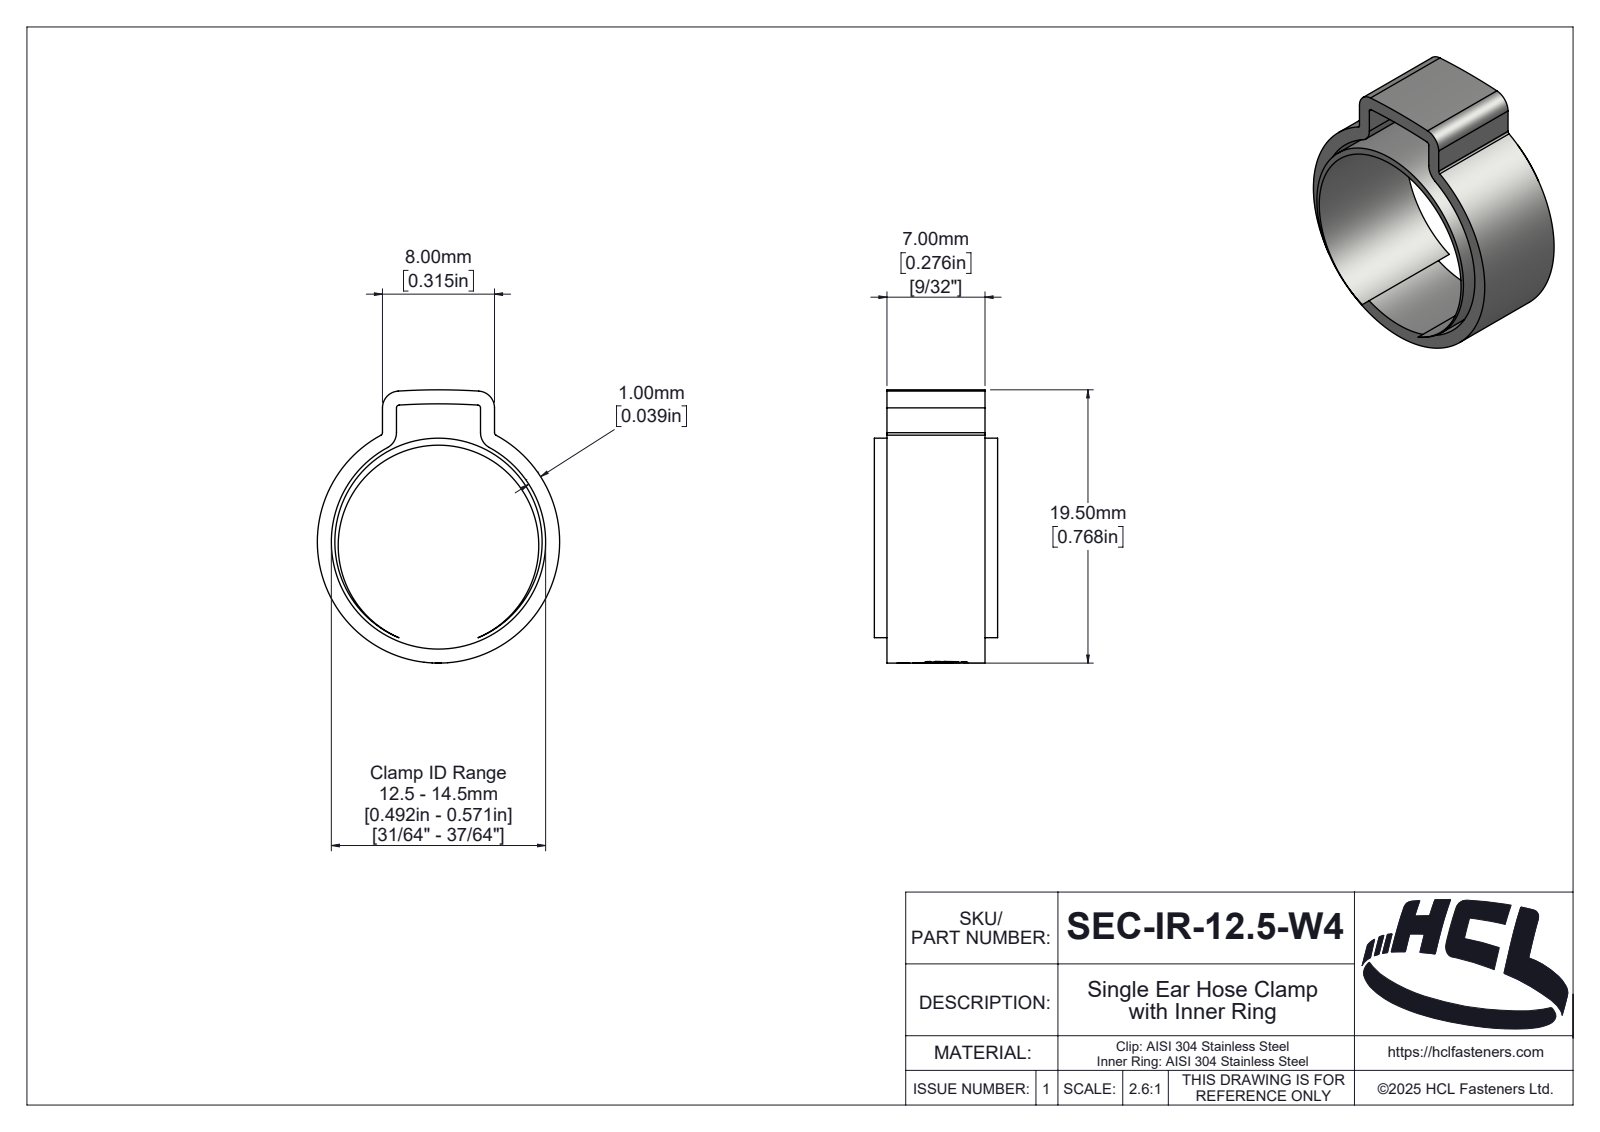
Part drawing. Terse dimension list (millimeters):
name: SEC-IR-12.5-W4
written by: SolidWorks 2025 (AUTOMOTIVE_DESIGN)
unit: mm
bodies: 2 solids, 131 faces (10 planar, 72 cylindrical, 49 other)
size: 19.5 × 17.3 × 8.8
volume: 489 mm³; area: 1 625 mm²
holes: 1× ⌀14.32, 1× ⌀15.3
bosses: 1× ⌀17.3, 1× ⌀14.8
rounds: 4× R0.2, 4× R1.2, 1× R0.21, 1× R0.88, 1× R1.09, 1× R1.15, 1× R1.39, 1× R1.97
face distances: 7, 1, 0.9, 7.9, 8, 6, 8.8, 3.71, 2.71, 3.29
